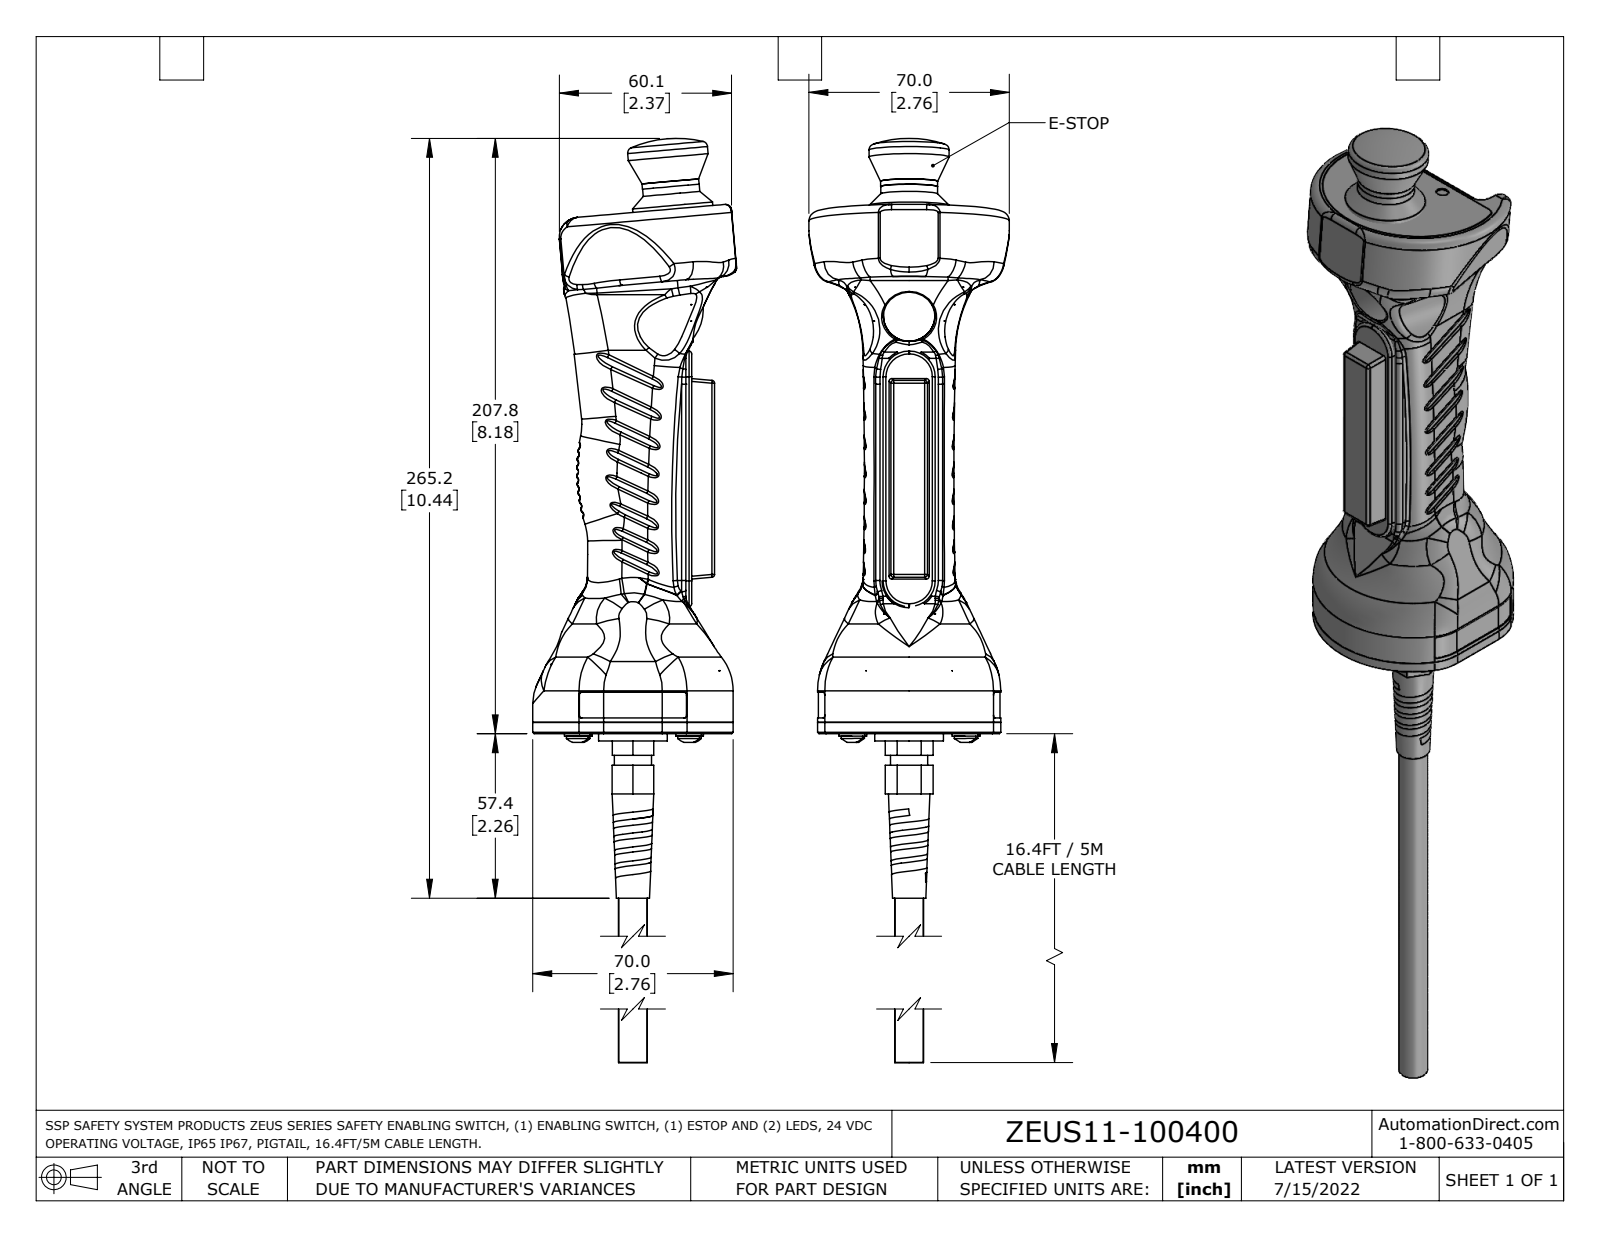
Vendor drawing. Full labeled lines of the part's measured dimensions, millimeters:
Part name (STEP PRODUCT): ZEUS11-100400
STEP written by: SolidWorks 2021 (AUTOMOTIVE_DESIGN)
Units: millimetres
Bodies: 20 solids, 1166 faces (333 planar, 407 cylindrical, 426 other)
Overall size (bounding box): 402.2 × 71.2 × 70
Volume: 416 900 mm³ · Surface area: 91 740 mm²
Round holes (diameter × count): ⌀3.4 ×4, ⌀4.3 ×4, ⌀4.5 ×4, ⌀5 ×4, ⌀2.5 ×2, ⌀2.8 ×2, ⌀4.2 ×2, ⌀4.4 ×2, ⌀8.4 ×2, ⌀10.6 ×1, ⌀14 ×1, ⌀18 ×1
Round bosses / shafts (diameter × count): ⌀9 ×4, ⌀7.5 ×4, ⌀4 ×4, ⌀1 ×4, ⌀28 ×2, ⌀19.8 ×2, ⌀6 ×2, ⌀4.6 ×2
Partial cylindrical surfaces — rounded edges, fillets, slot ends (radius × count): R0.1 ×96, R1 ×51, R0.7 ×48, R2 ×21, R3 ×10, R0.8 ×7, R0.3 ×5, R15.7 ×4
Main face-to-face distances: 4, 2, 0.5, 0.4, 1.7, 1.5, 2.5, 4.5, 14.5, 4.1
Hole centre spacings: 10.3, 16, 22, 27.4, 30, 38.9, 39.6, 13
